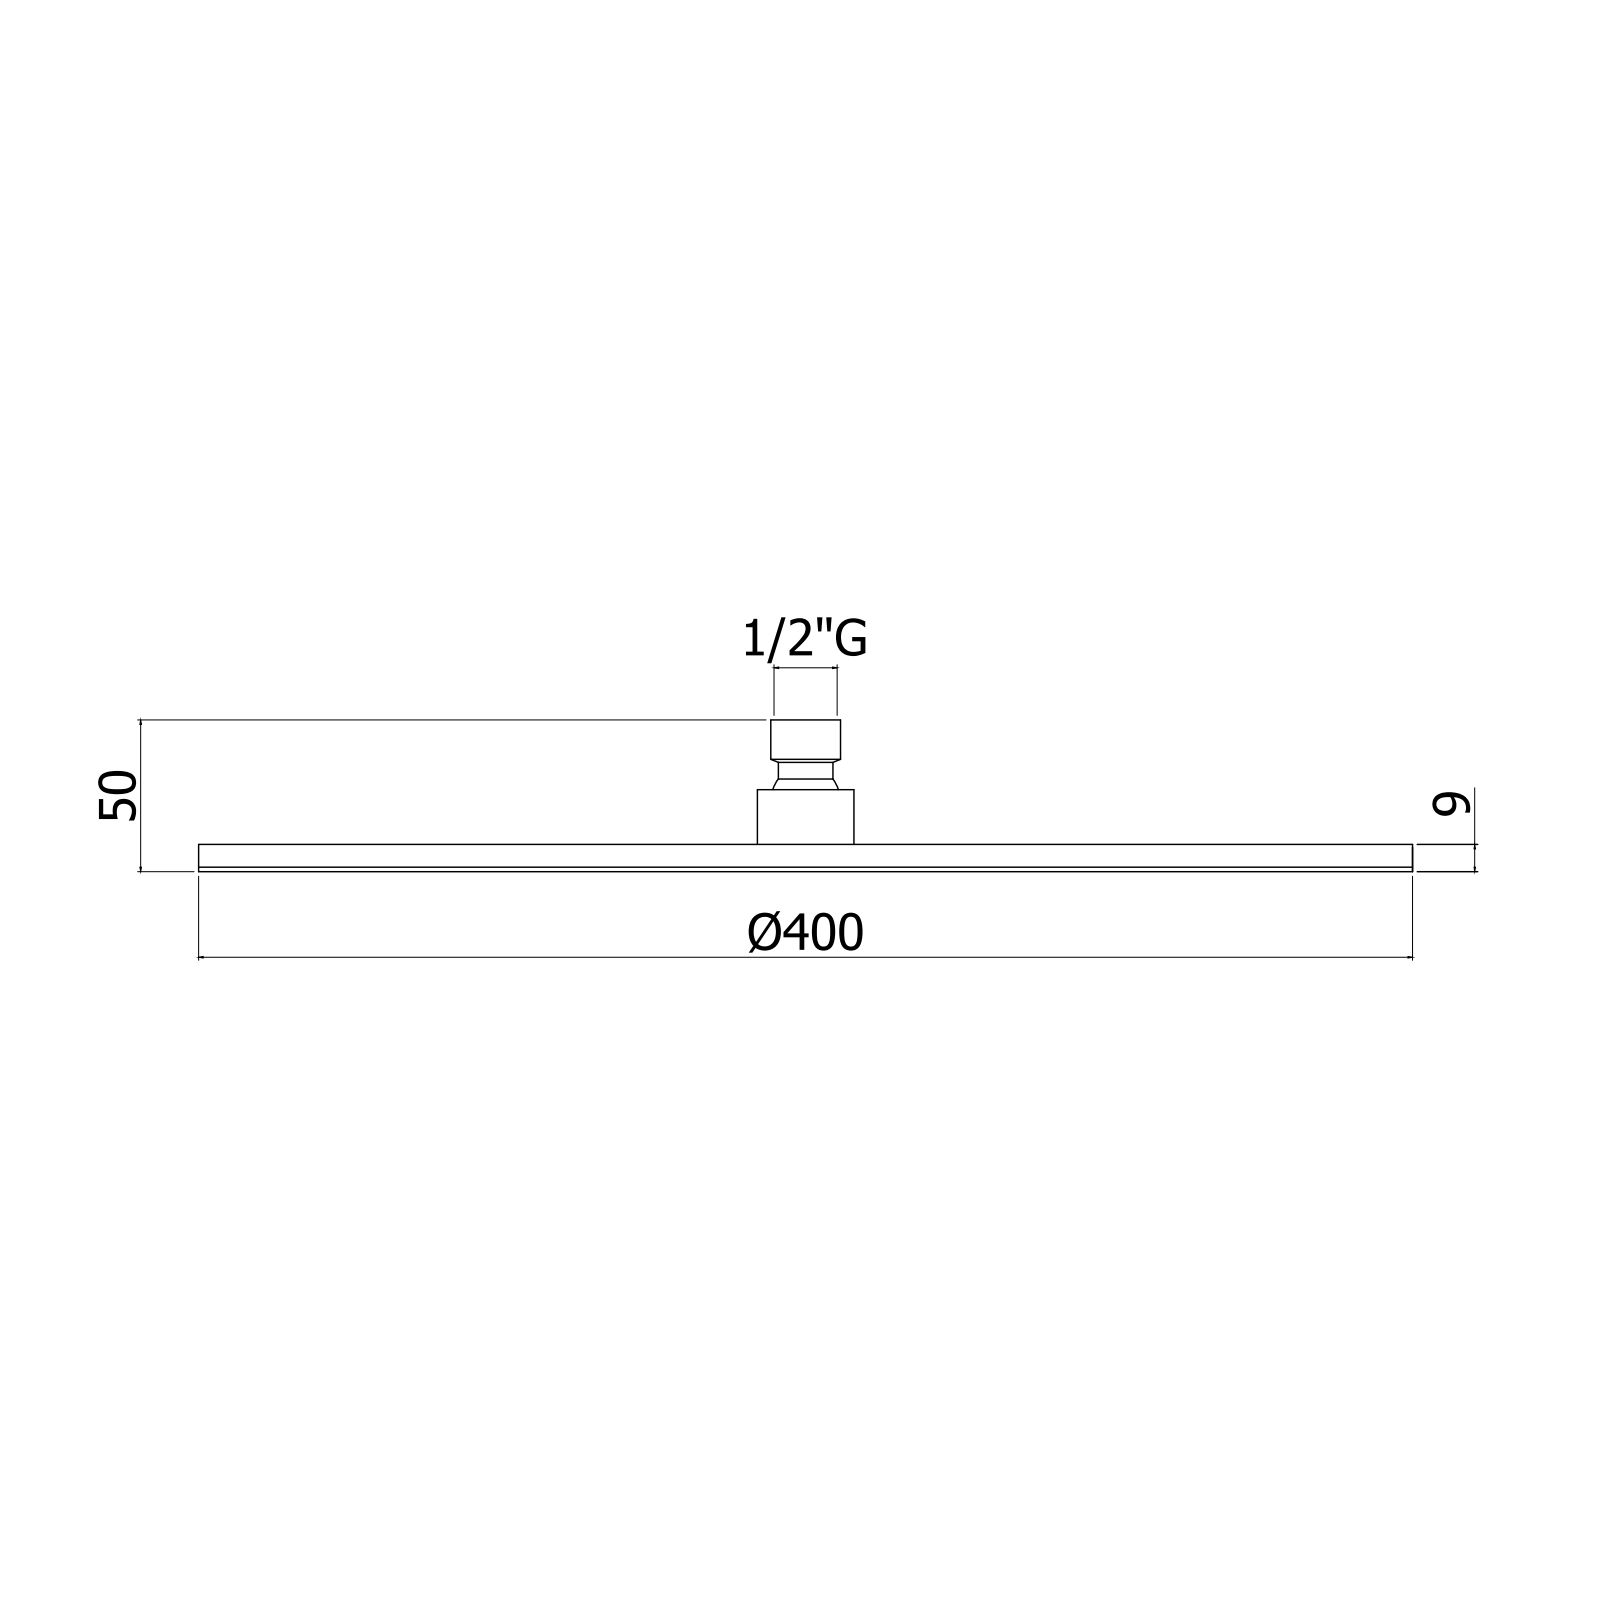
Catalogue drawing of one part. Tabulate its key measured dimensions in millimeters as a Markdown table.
| quantity | value |
| --- | --- |
| part name | ZSOF082CR |
| STEP written by | CREO PARAMETRIC BY PTC INC, 2020044 (CONFIG_CONTROL_DESIGN) |
| units | millimeters |
| bodies | 1 solid, 5175 faces (618 planar, 1246 cylindrical, 3311 other) |
| overall size | 400.2 × 400.2 × 51.9 |
| volume | 488 421 mm³ |
| surface area | 505 903 mm² |
| round holes (diameter × count) | 1.5 × 156, 1.7 × 156, 7 × 17, 2.5 × 16, 5.1 × 16, 6 × 16, 15 × 1, 16 × 1, 16.5 × 1, 18.63 × 1, 23.1 × 1, 23.8 × 1 |
| round bosses / shafts (diameter × count) | 10 × 156, 5 × 16, 400.2 × 1, 400 × 1, 395.6 × 1, 31.8 × 1, 28 × 1, 23.2 × 1 |
| partial cylindrical surfaces (radius × count) | 20 × 16 |
| main face-to-face distances | 8.5, 7.5, 1, 1.5, 6, 7, 5.6, 2.9, 1.4, 4.6 |
| hole center spacings | 170, 146.57, 191.5, 270.82, 353.85, 375.64, 59.04, 74.72 |
